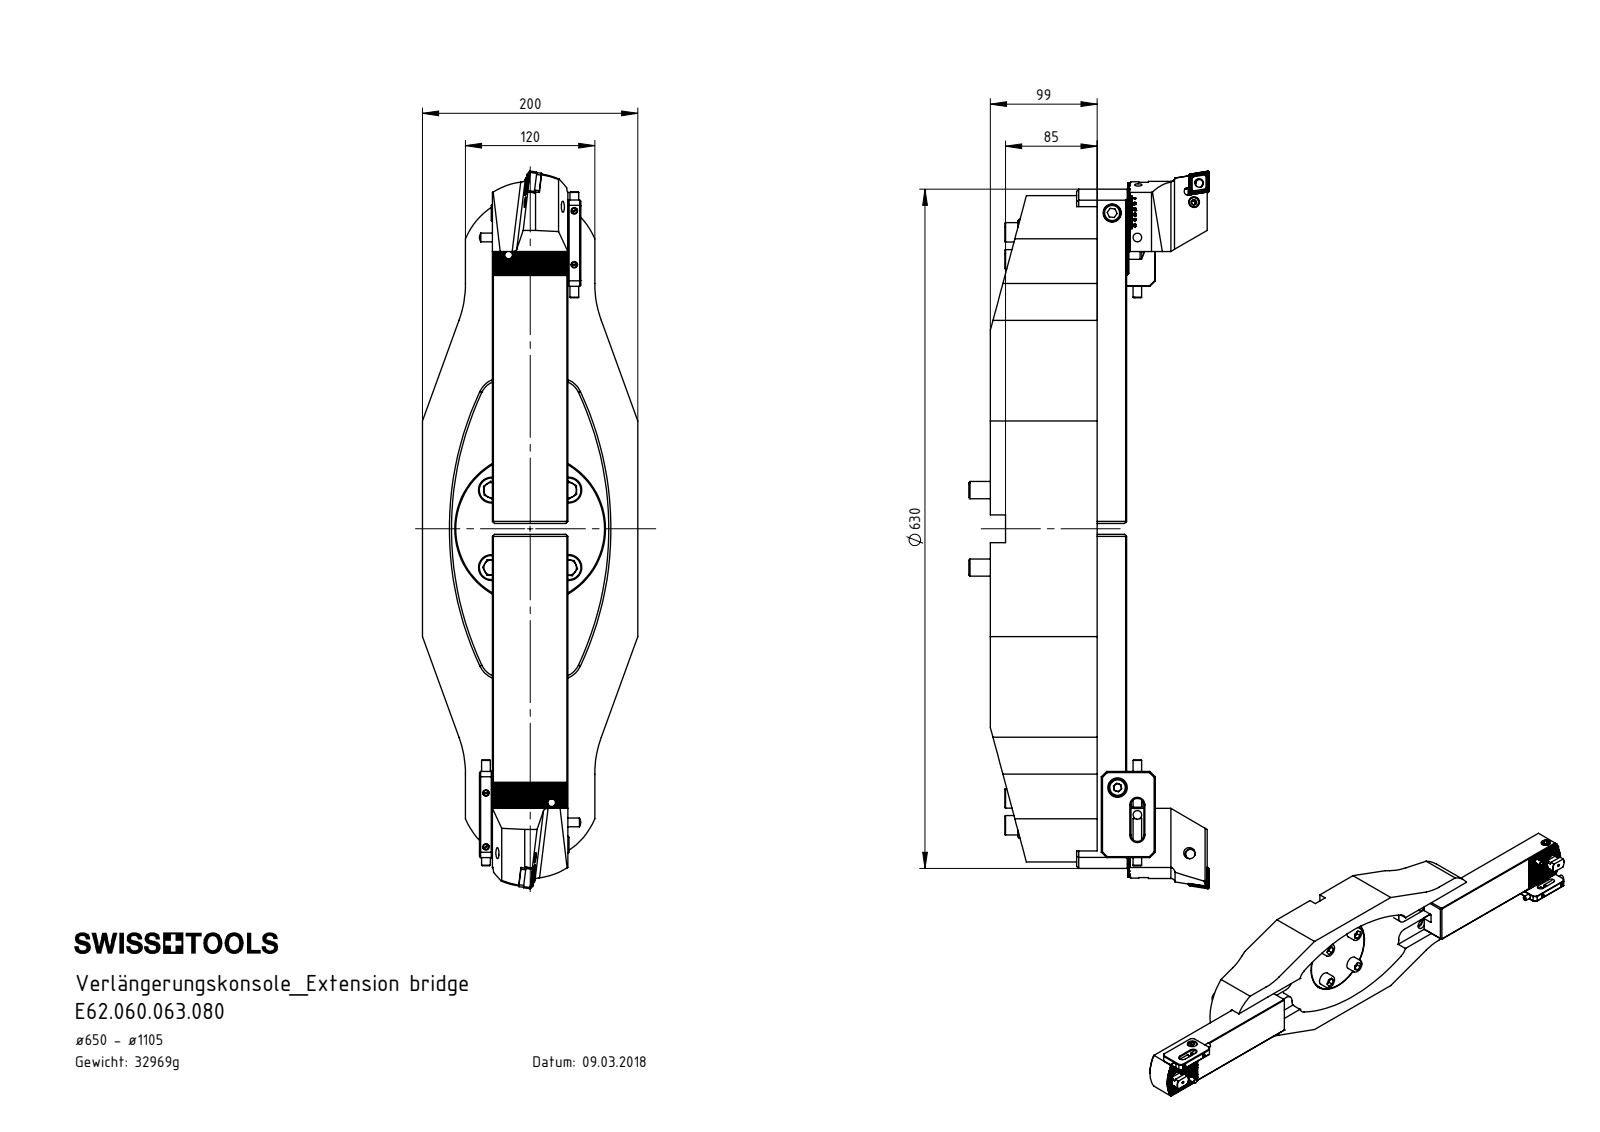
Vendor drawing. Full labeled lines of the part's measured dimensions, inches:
Part name (STEP PRODUCT): VK3-VK1.310.048_B; VK3-VK1.310.048; DIN 179 - D12xD18x12; E62.060.063.080 (+8 more)
STEP written by: SolidWorks 2017 (CONFIG_CONTROL_DESIGN)
Units: inches
Bodies: 86 solids, 3665 faces (1810 planar, 950 cylindrical, 905 other)
Overall size (bounding box): 26.204 × 8.788 × 7.874
Volume: 524.6 in³ · Surface area: 1 463 in²
Round holes (diameter × count): ⌀0.709 ×40, ⌀0.402 ×34, ⌀0.512 ×16, ⌀0.268 ×6, ⌀0.315 ×6, ⌀0.472 ×6, ⌀0.197 ×4, ⌀0.236 ×4, ⌀0.669 ×4, ⌀0.079 ×2, ⌀0.313 ×2, ⌀0.335 ×2
Round bosses / shafts (diameter × count): ⌀0.945 ×19, ⌀0.472 ×9, ⌀0.63 ×8, ⌀0.394 ×4, ⌀0.236 ×4, ⌀0.709 ×2, ⌀0.39 ×2, ⌀0.339 ×2
Partial cylindrical surfaces — rounded edges, fillets, slot ends (radius × count): R0.006 ×55, R0.079 ×20, R0.047 ×8, R0.071 ×8, R0.163 ×8, R0.866 ×8, R0.591 ×6, R2.559 ×6
Main face-to-face distances: 1.732, 0.787, 0.984, 2.362, 5.315, 2.559, 3.15, 3.898, 1.535, 0.748
Hole centre spacings: 0.984, 1.857, 1.575, 1.969, 2.521, 18.701, 18.767, 5.906
